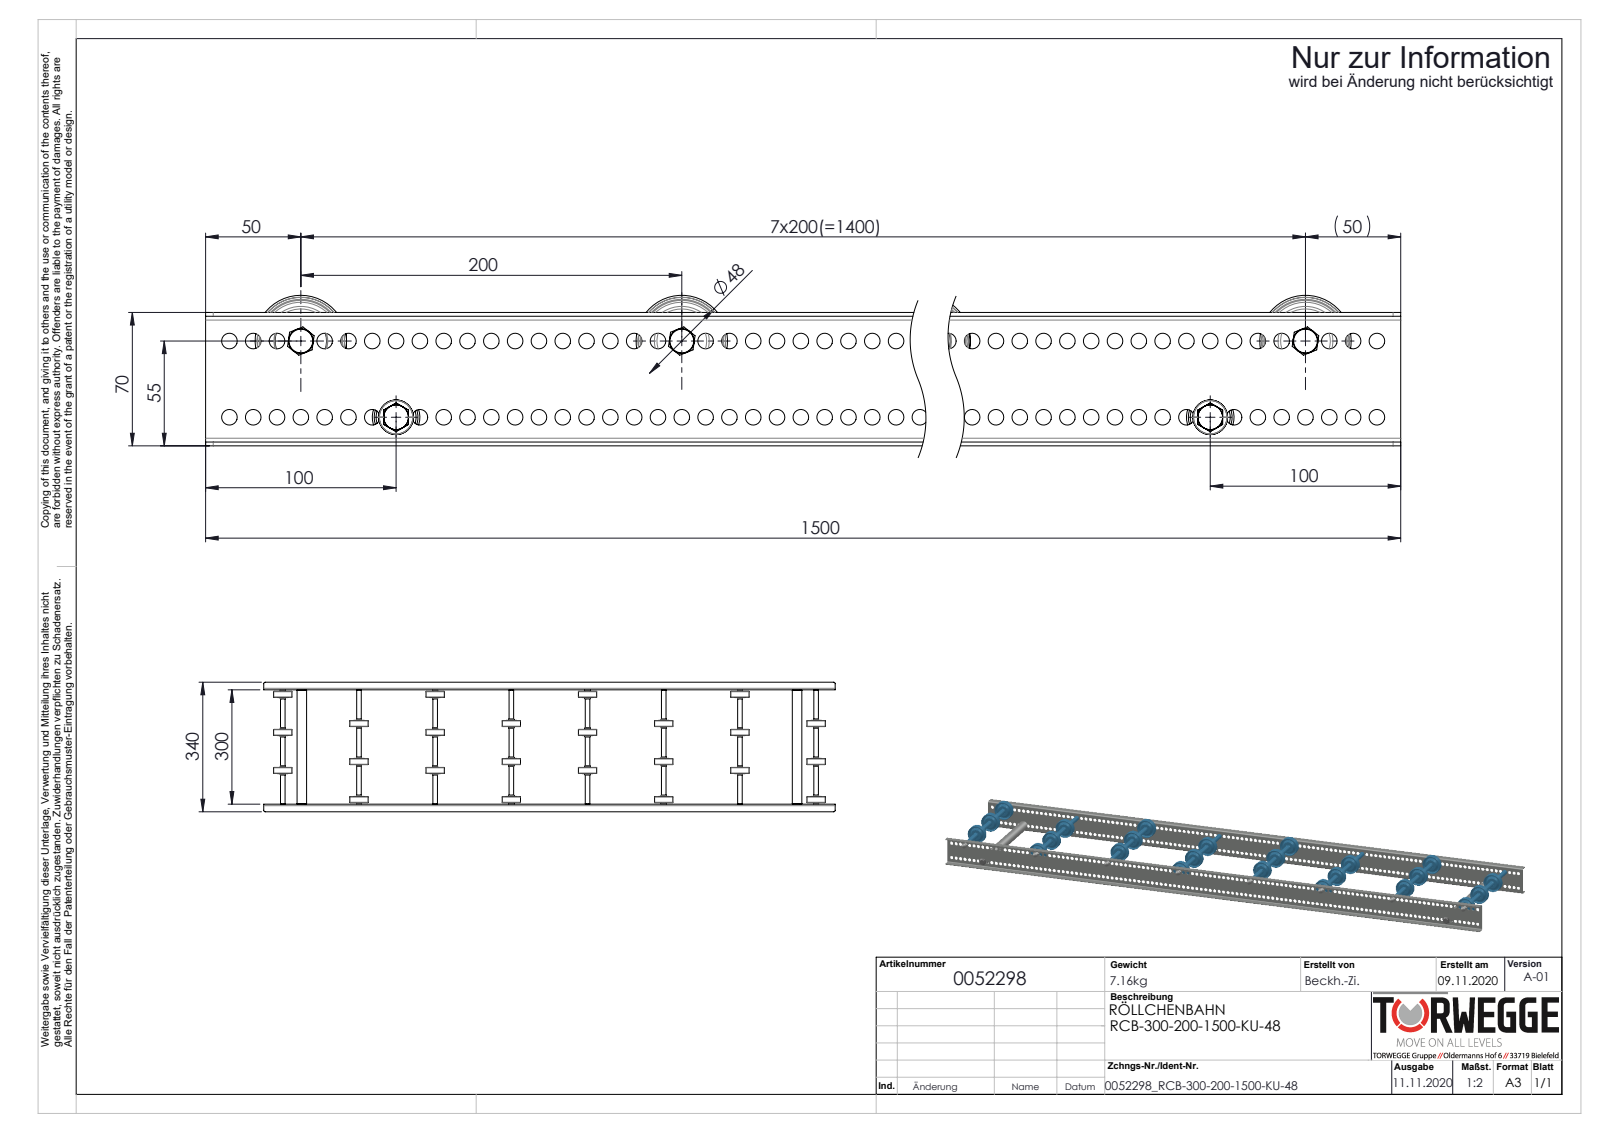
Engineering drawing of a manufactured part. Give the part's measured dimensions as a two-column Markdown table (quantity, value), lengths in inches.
| quantity | value |
| --- | --- |
| part name | Hutmutter_DIN_1587_M8; Röllchenachse-für-Konfiguration_EL300; S100994_Sperrzahnschraube_M08x16-8.8-A2K; Traversen_KFG_L300 (+5 more) |
| STEP written by | SolidWorks 2020 (AUTOMOTIVE_DESIGN) |
| units | inches |
| bodies | 84 solids, 3544 faces (576 planar, 1616 cylindrical, 1352 other) |
| overall size | 59.055 × 13.386 × 3.11 |
| volume | 82.99 in³ |
| surface area | 1 770 in² |
| round holes (diameter × count) | 0.323 × 238, 0.262 × 8, 0.38 × 8, 0.539 × 8, 0.268 × 2, 0.827 × 2 |
| round bosses / shafts (diameter × count) | 0.315 × 10, 1.89 × 8, 1.063 × 8, 0.5 × 8, 0.492 × 8, 0.472 × 8, 0.984 × 2 |
| partial cylindrical surfaces (radius × count) | 0.157 × 8, 0.079 × 4 |
| main face-to-face distances | 0.079, 11.89, 2.677, 11.969, 11.811, 2.756, 2.598, 3.929, 0.709, 0.787 |
| hole center spacings | 0.492, 0.984, 1.476, 1.969, 2.461, 2.953, 3.445, 3.937 |
